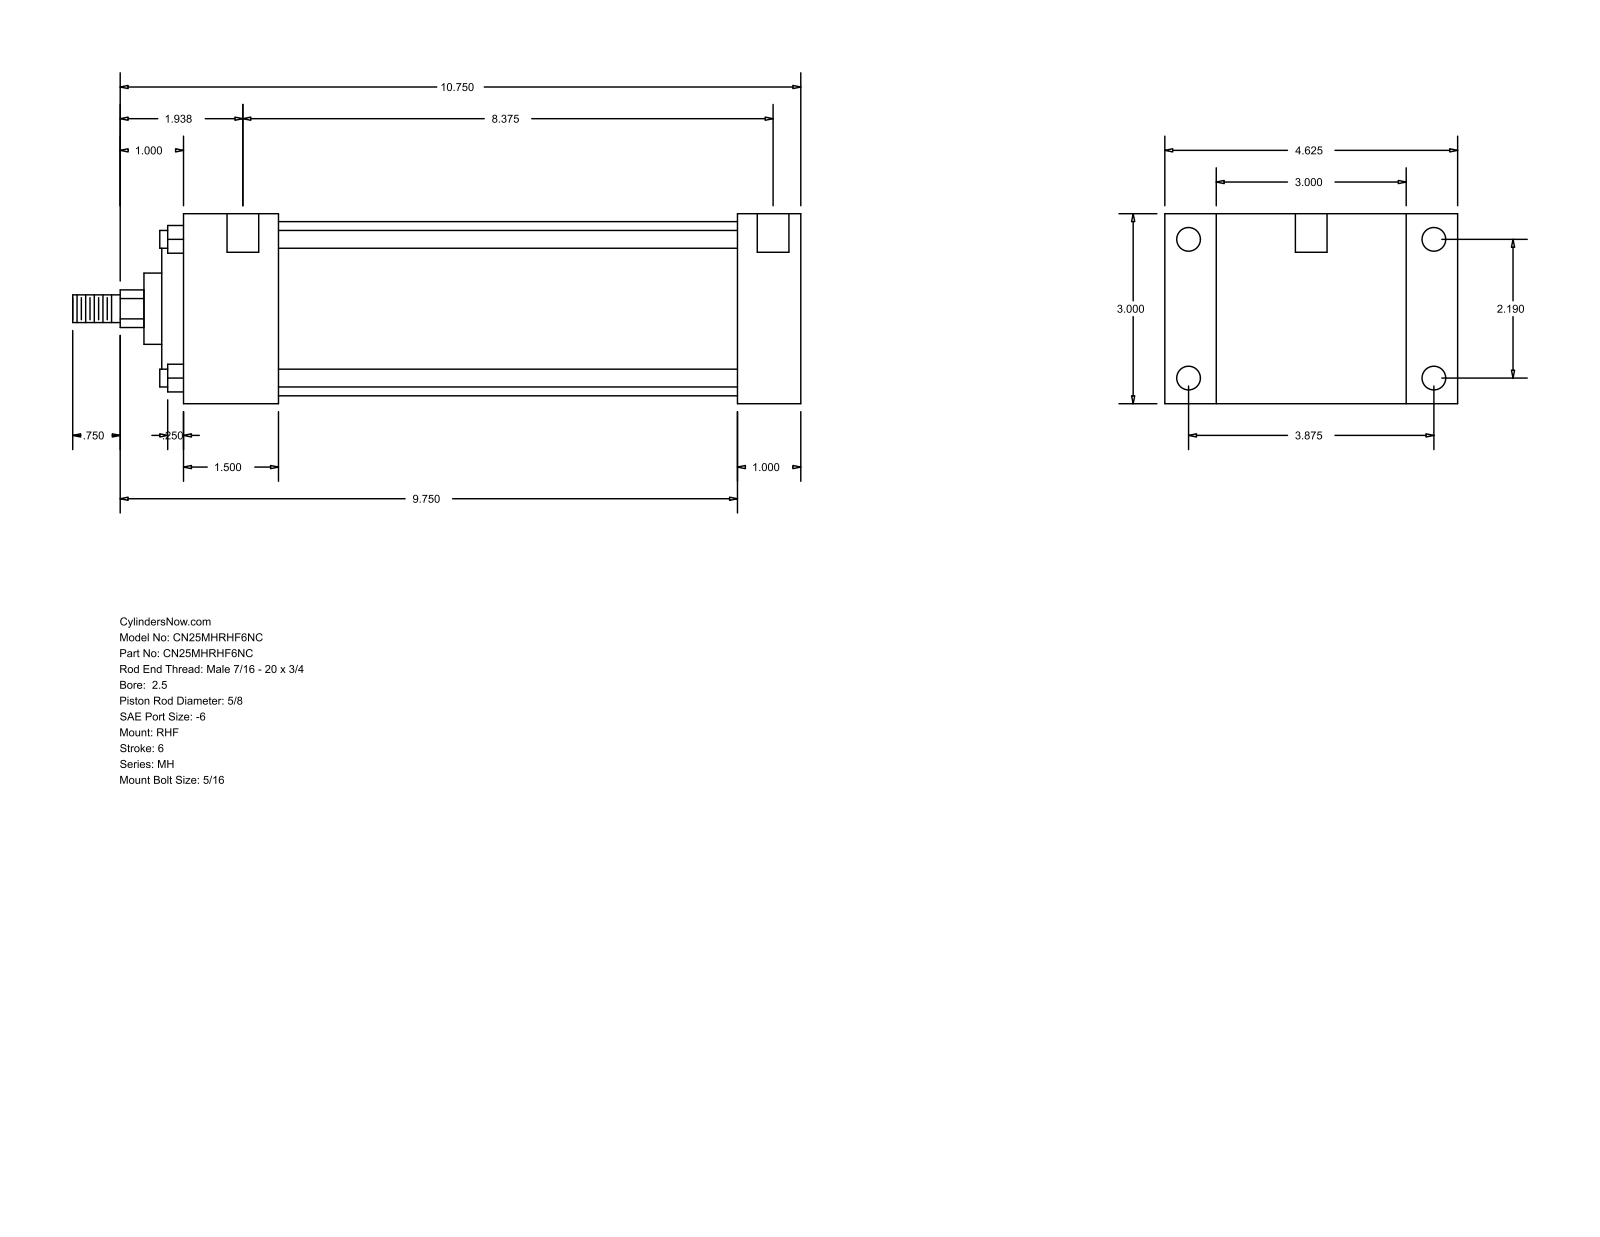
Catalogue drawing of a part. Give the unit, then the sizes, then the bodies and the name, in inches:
Units: inches
Overall size (bounding box): 11.5 × 4.625 × 3
Round holes (diameter × count): ⌀0.219 ×4, ⌀0.375 ×4, ⌀0.5 ×2
Round bosses / shafts (diameter × count): ⌀0.281 ×4, ⌀2.75 ×1, ⌀2.187 ×1, ⌀1.125 ×1, ⌀0.625 ×1, ⌀0.437 ×1
Partial cylindrical surfaces — rounded edges, fillets, slot ends (radius × count): R0.297 ×1
Main face-to-face distances: 3, 1, 0.813, 3.813, 9.75, 8.75, 1.5, 4.625, 7.25, 8.25
Hole centre spacings: 2.19, 3.875, 4.451, 8.687, 0.125, 0.187, 8.375, 8.5
Bodies: 0 solids, 90 faces (61 planar, 29 cylindrical, 0 other)
Part name (STEP PRODUCT): MH_RHF__0250_0.625
STEP written by: GSSL Pune (CONFIG_CONTROL_DESIGN)
